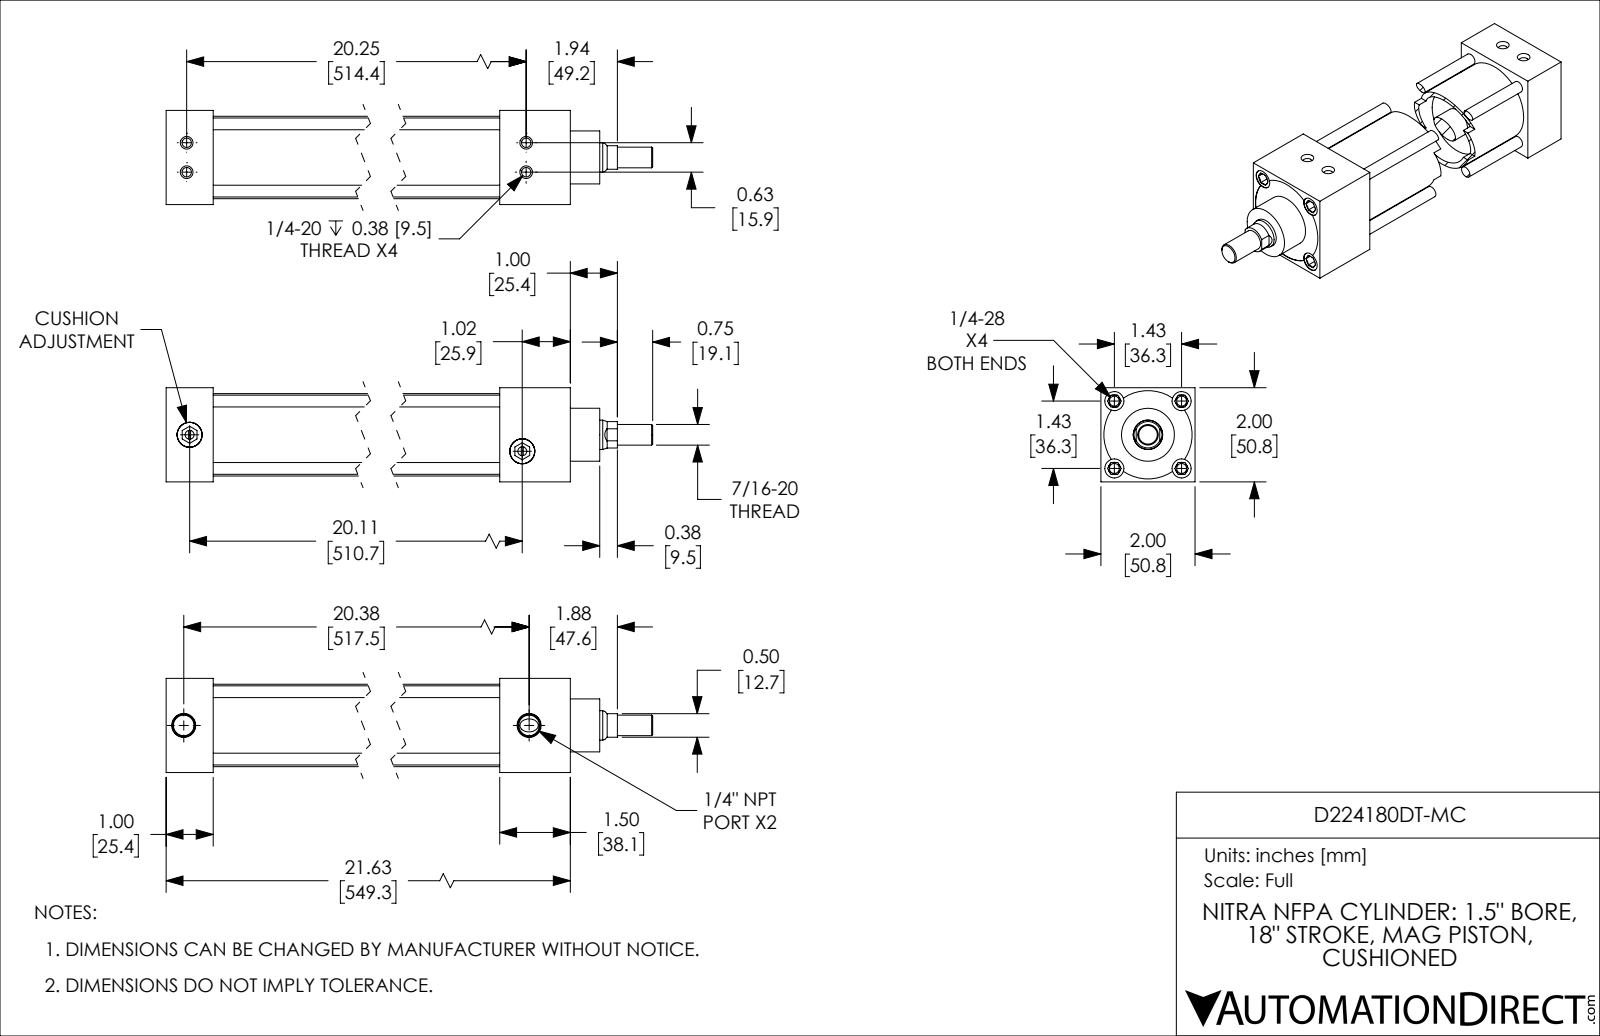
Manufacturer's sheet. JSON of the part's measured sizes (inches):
{"part_name": "D224180DT-MC; D224180DT-MC_CUSHION; D224180DT-MC_PISTON_KK1; D224180DT-MC_BODY", "step_written_by": "SolidWorks 2019 (CONFIG_CONTROL_DESIGN)", "units": "inches", "bodies": {"solids": 4, "faces": 251, "planar": 90, "cylindrical": 81, "other": 80}, "overall_size": [23.375, 2, 2], "volume_in3": 33.71, "surface_area_in2": 354.6, "round_holes": [[0.201, 4], [0.213, 4], [0.406, 4], [0.19, 2], [0.438, 2], [0.531, 2], [0.626, 1], [1.501, 1]], "round_bosses_or_shafts": [[0.25, 4], [0.532, 2], [1.751, 1], [1.499, 1], [1.125, 1], [0.624, 1], [0.437, 1]], "partial_cylinders_radius": [[0.281, 1], [0.937, 1]], "face_to_face_distances": [2, 1, 20.125, 19.125, 2.125, 21.62, 20.62, 1.495, 1.125, 18], "hole_center_spacings": [0.319, 1.011, 1.43, 0.625, 2.022, 20.25, 20.26, 20.315]}
